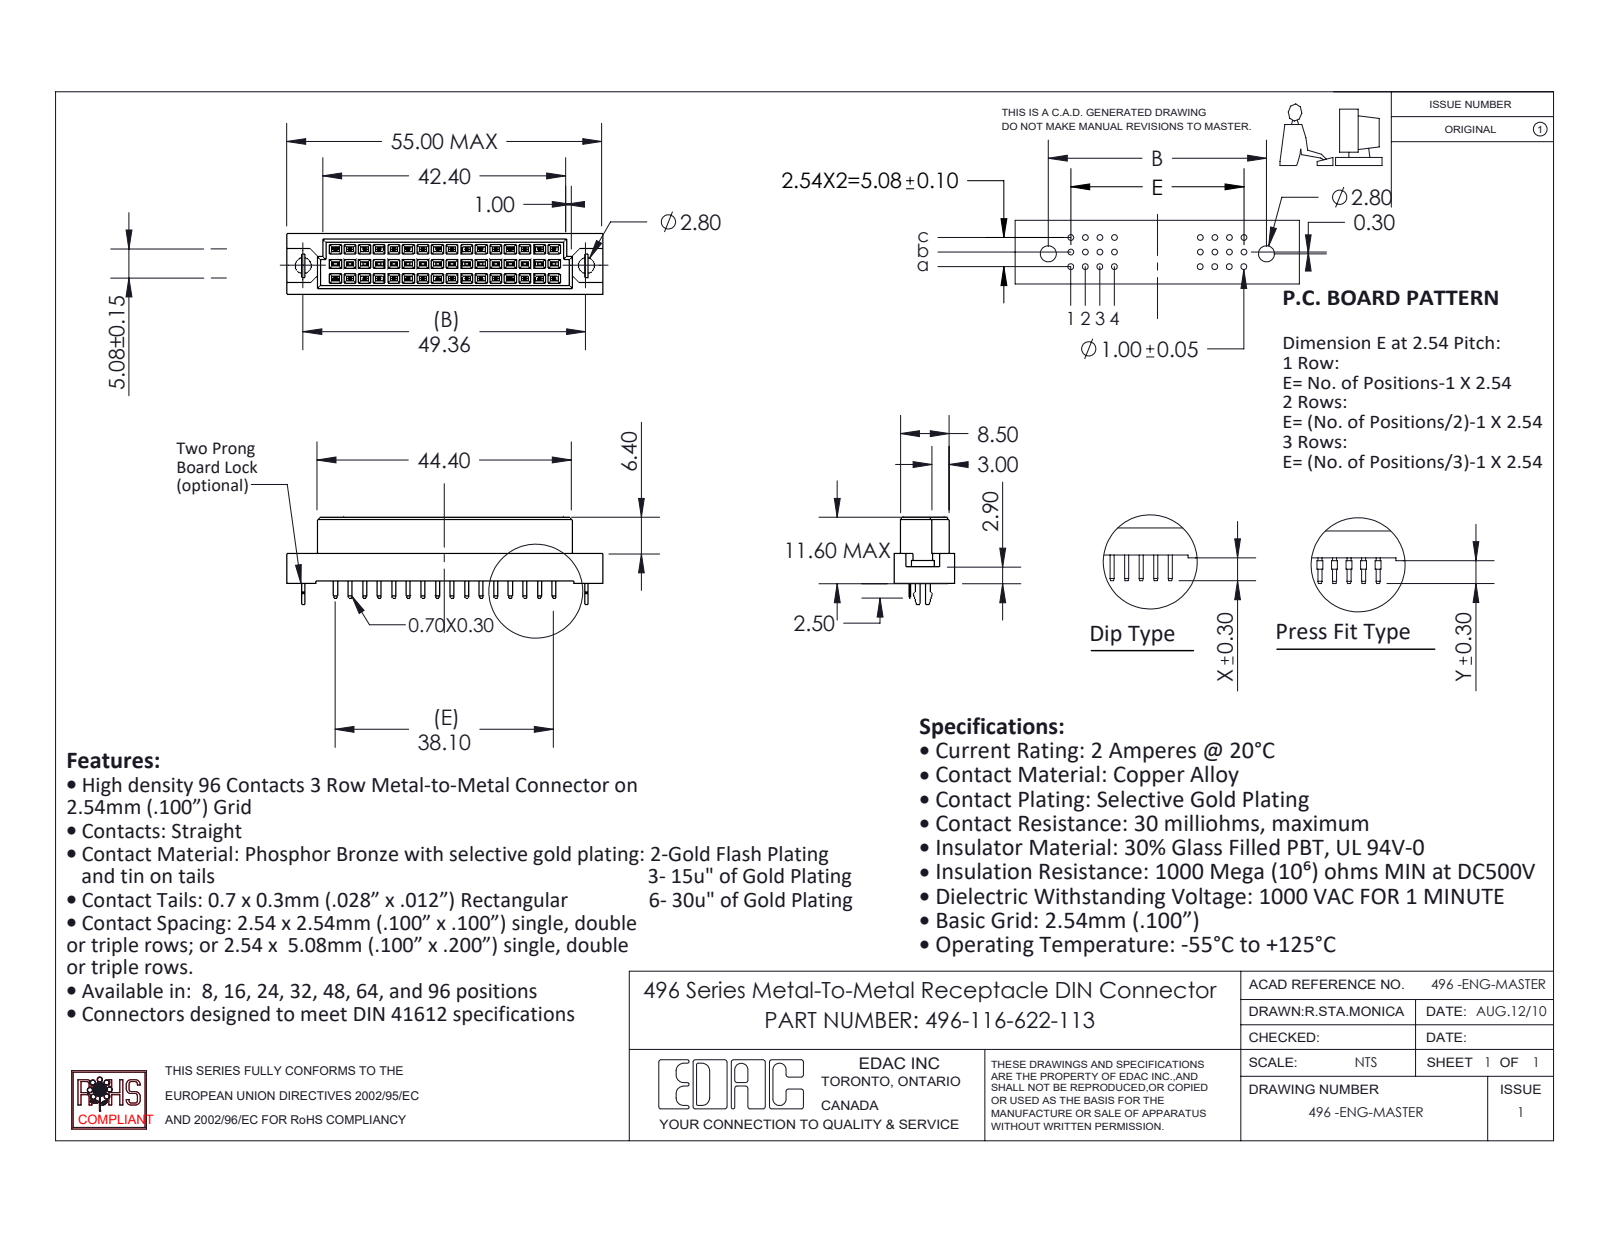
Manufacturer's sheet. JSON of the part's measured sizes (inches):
{"part_name": "496-116-622-113; 496 Part_48; 496 Bore-lock; 496-290_22", "step_written_by": "SolidWorks 2020 (CONFIG_CONTROL_DESIGN)", "units": "inches", "bodies": {"solids": 19, "faces": 862, "planar": 856, "cylindrical": 6, "other": 0}, "overall_size": [2.165, 0.598, 0.417], "volume_in3": 0.283, "surface_area_in2": 7.057, "round_holes": [[0.11, 2]], "partial_cylinders_radius": [[0.021, 1]], "face_to_face_distances": [0.1, 0.041, 0.376, 0.2, 0.032, 0.417, 0.132, 0.068, 0.335, 0.022], "hole_center_spacings": [1.943]}
